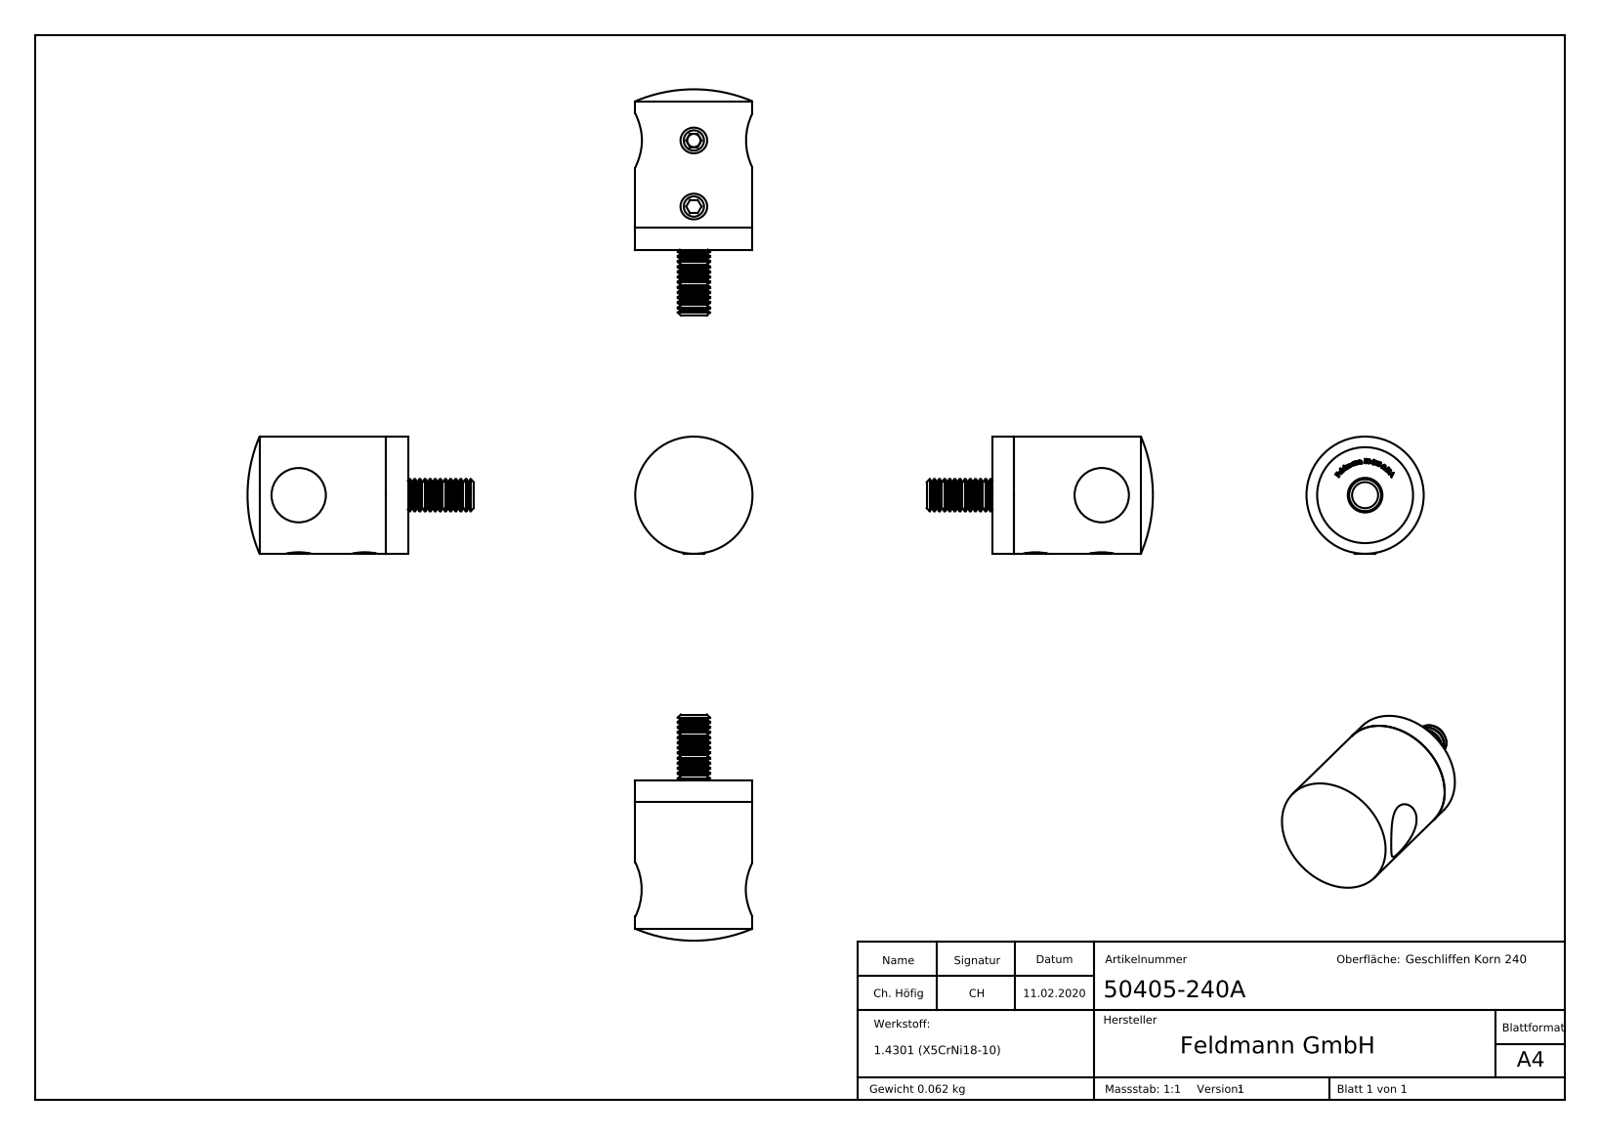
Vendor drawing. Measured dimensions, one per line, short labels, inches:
name: socket countersunk head screw_din; DIN914_DIN 914 M5x6; 50405-240A; socket countersunk head screw_din_DIN 7991 - M6 x 25 --- 25S (+7 more)
written by: SolidWorks 2015 (CONFIG_CONTROL_DESIGN)
unit: in
bodies: 5 solids, 375 faces (185 planar, 35 cylindrical, 155 other)
size: 2.756 × 1.671 × 0.866
volume: 0.52 in³; area: 9.25 in²
holes: 2× ⌀0.165, 1× ⌀0.256, 1× ⌀0.402, 1× ⌀0.472, 1× ⌀0.709
bosses: 2× ⌀0.197, 1× ⌀0.866, 1× ⌀0.469, 1× ⌀0.456, 1× ⌀0.236
face distances: 0.083, 0.079, 0.161, 0.498, 0.419, 0.337, 0.098, 0.457, 0.378, 0.295
hole spacings: 0.488
